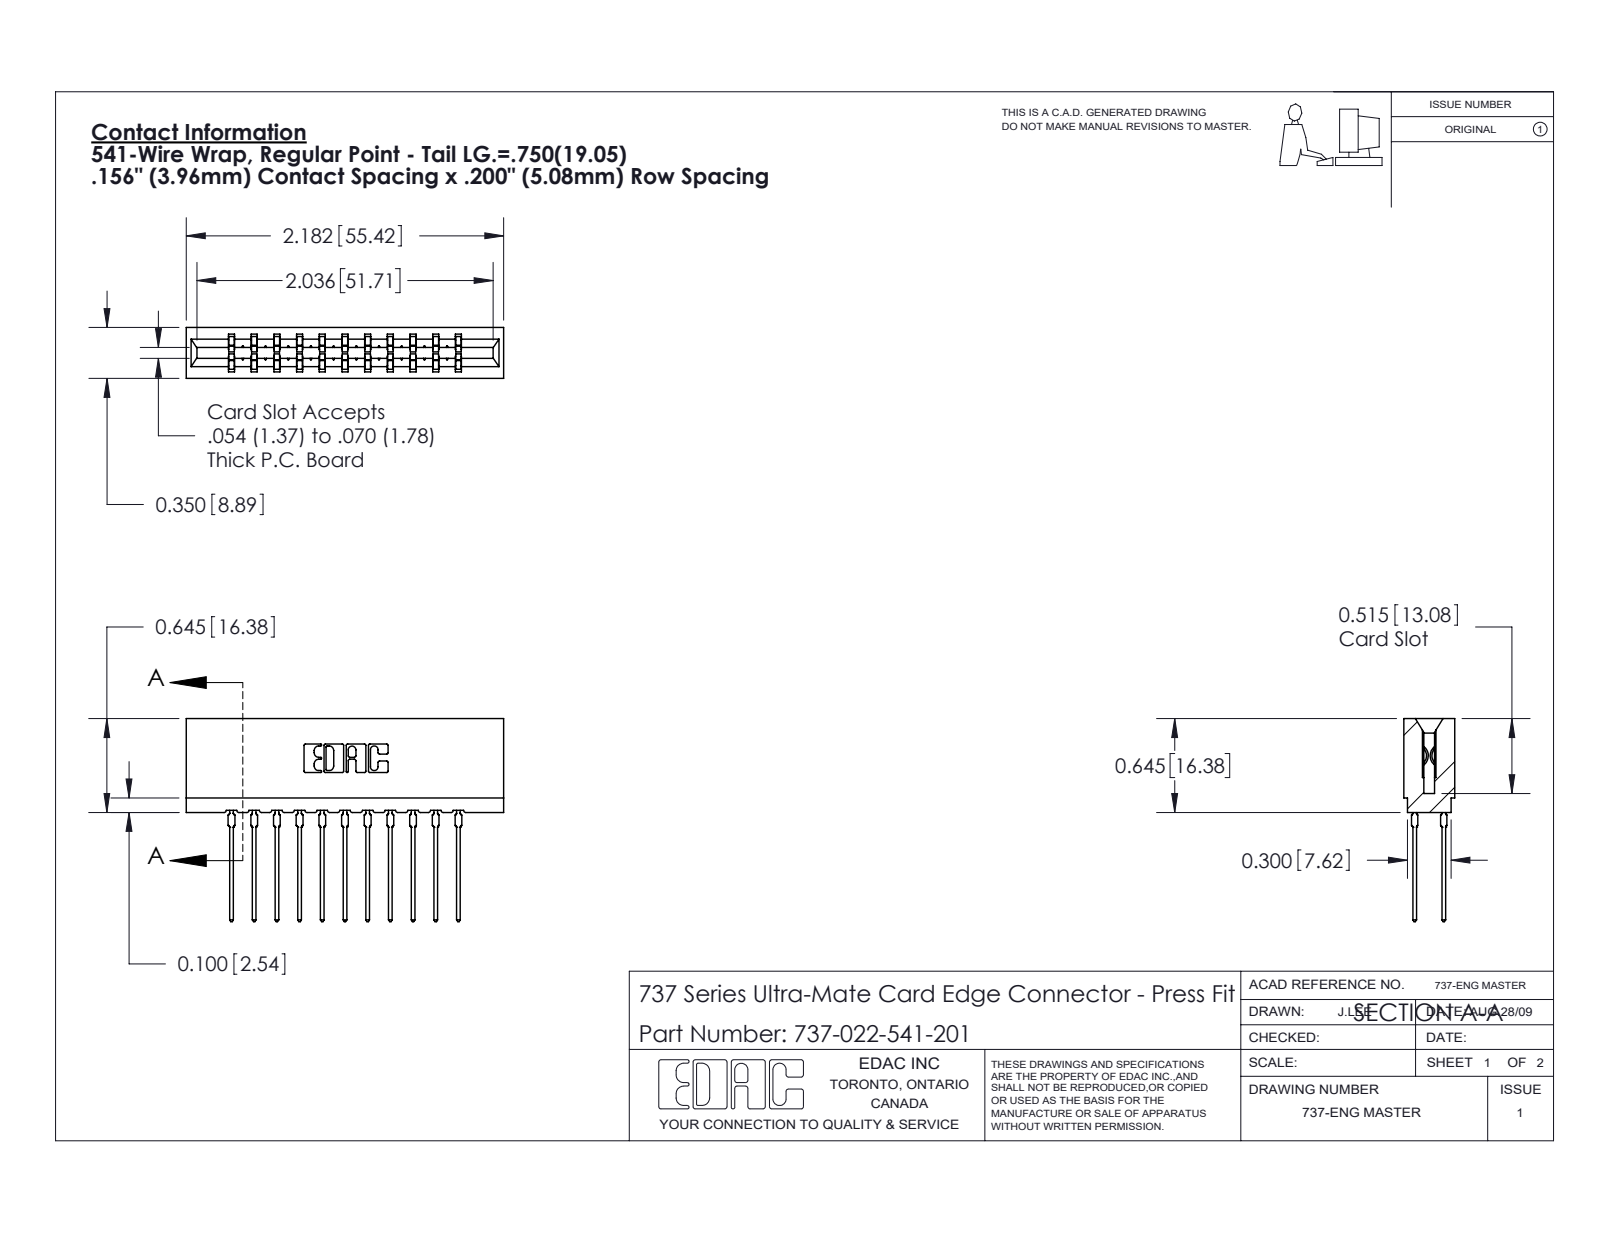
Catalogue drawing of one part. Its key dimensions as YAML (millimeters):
part_name: "745-292-001_541; 737-022-541-201; 737 Part_Insulator Option - 01"
step_written_by: "SolidWorks 2020 (CONFIG_CONTROL_DESIGN)"
units: millimeters
bodies: {solids: 23, faces: 2074, planar: 1077, cylindrical: 425, other: 572}
overall_size: [55.4, 35.5, 8.9]
volume: 5780
surface_area: 8206
partial_cylinders:
  - {radius: 0.5, count: 44}
  - {radius: 0.3, count: 22}
  - {radius: 0.4, count: 22}
  - {radius: 0.1, count: 8}
  - {radius: 0.3, count: 8}
  - {radius: 0.2, count: 6}
  - {radius: 0.8, count: 6}
  - {radius: 0.7, count: 3}
face_to_face_distances: [3.5, 5.4, 4, 8.9, 15.8, 7.9, 11.9, 1.6, 7.3, 1.9]
